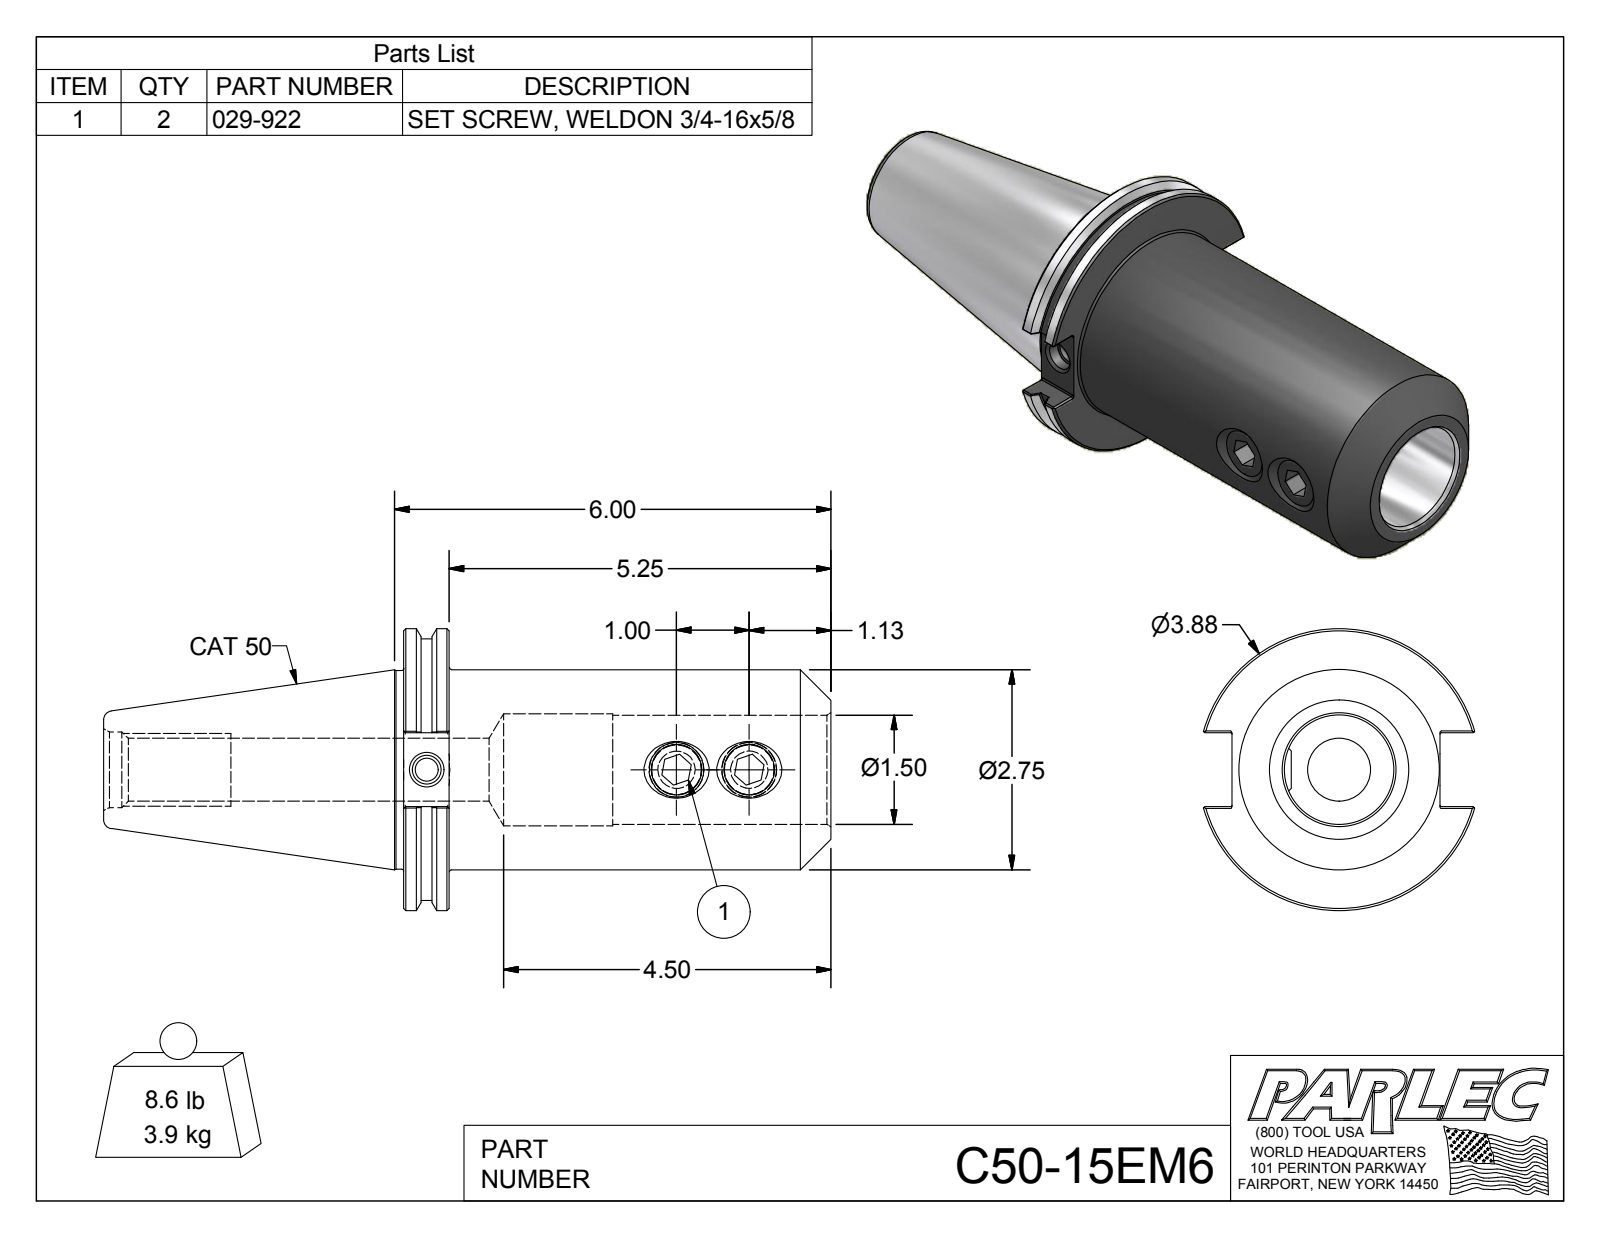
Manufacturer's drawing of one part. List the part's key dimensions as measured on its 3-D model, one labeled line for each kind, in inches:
Part name (STEP PRODUCT): C50-15EM6; C50-15EM6-1; 029-922
STEP written by: Autodesk Inventor 2012 (AUTOMOTIVE_DESIGN)
Units: inches
Bodies: 3 solids, 114 faces (50 planar, 30 cylindrical, 34 other)
Overall size (bounding box): 10 × 3.875 × 3.729
Volume: 41.16 in³ · Surface area: 140.4 in²
Round holes (diameter × count): ⌀0.687 ×2, ⌀0.315 ×1, ⌀0.399 ×1, ⌀0.865 ×1, ⌀1.038 ×1, ⌀1.5 ×1, ⌀1.54 ×1
Round bosses / shafts (diameter × count): ⌀0.75 ×2, ⌀3.875 ×1, ⌀3.594 ×1, ⌀2.75 ×1, ⌀2.73 ×1
Partial cylindrical surfaces — rounded edges, fillets, slot ends (radius × count): R0.02 ×12
Main face-to-face distances: 0.625, 5.875, 5.25, 2.669, 4.125, 4.75, 10, 0.375, 2.86, 0.191
Hole centre spacings: 1, 3.435, 4.435
